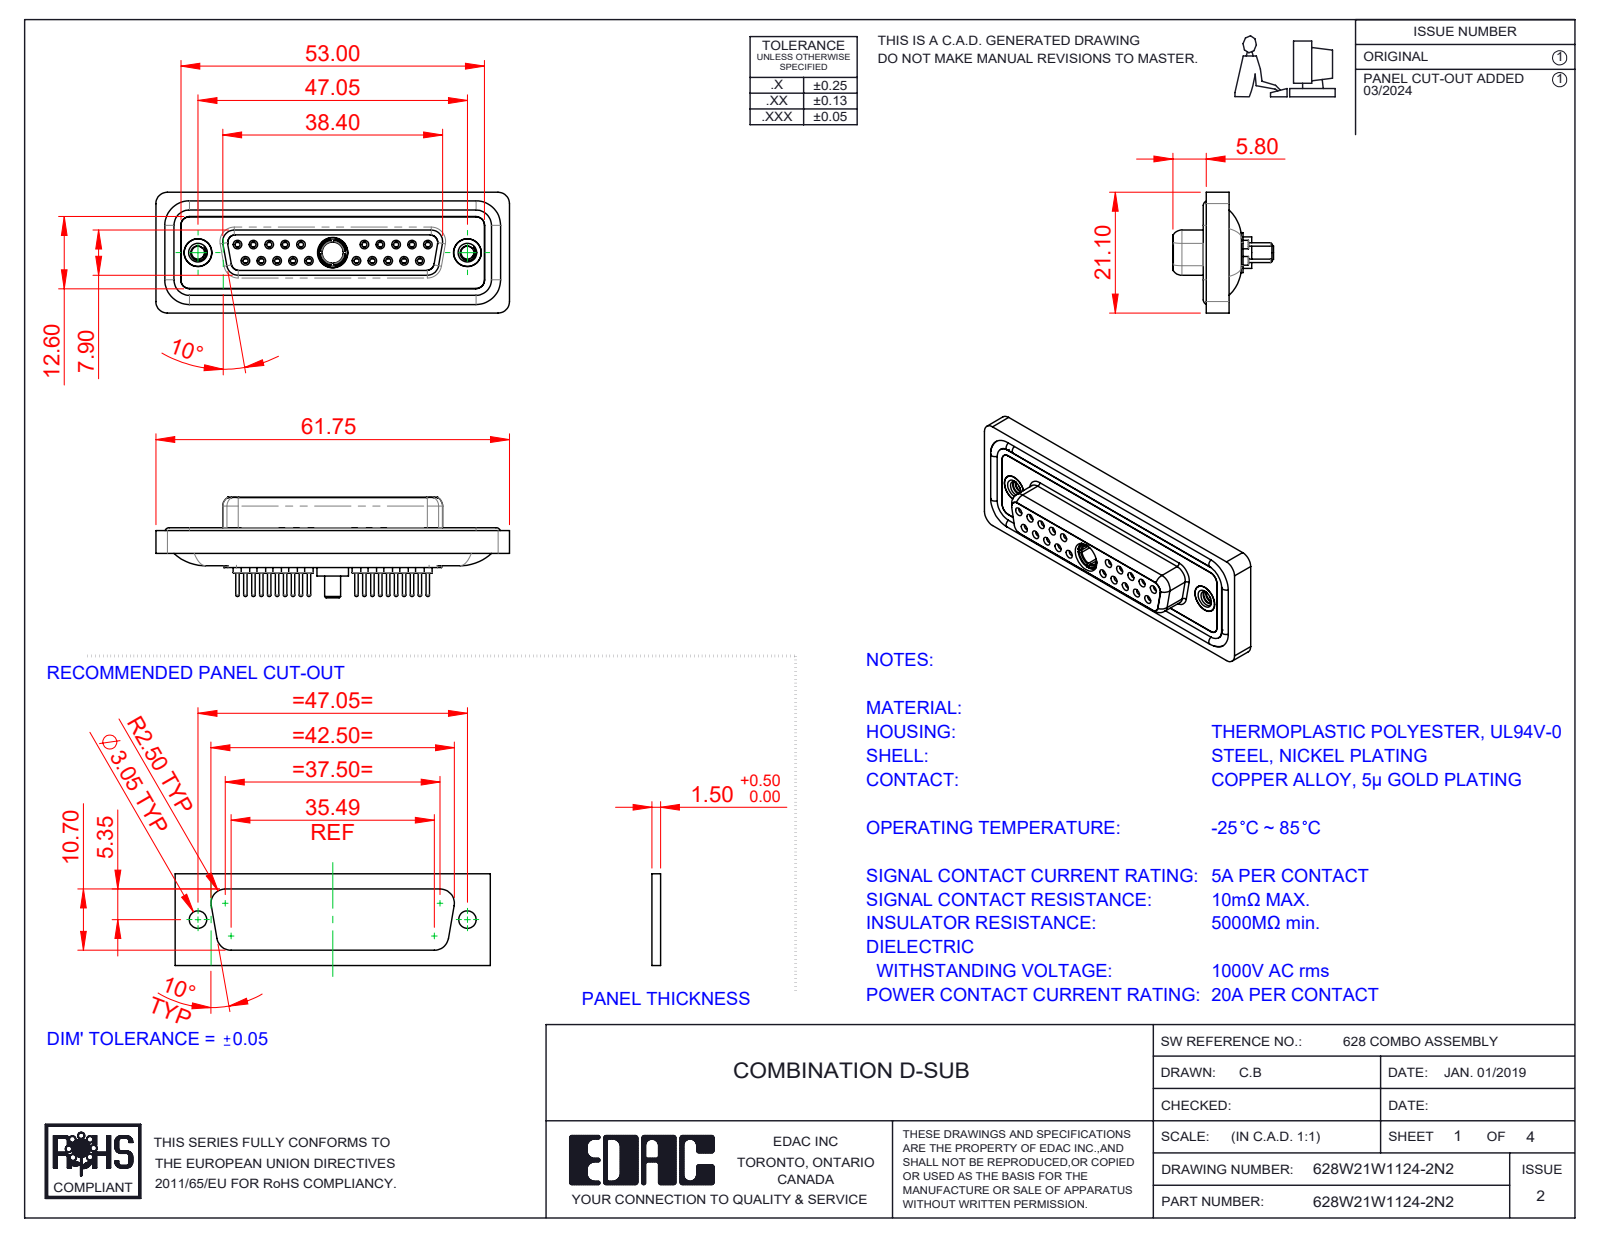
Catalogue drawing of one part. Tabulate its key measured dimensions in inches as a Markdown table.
| quantity | value |
| --- | --- |
| part name | 628Combo Contact Row 2_24; 628Combo Shell Front_25 Contacts; Power Socket_20A S; 628W21W1124-2N2 (+5 more) |
| STEP written by | SolidWorks 2023 (CONFIG_CONTROL_DESIGN) |
| units | inches |
| bodies | 29 solids, 1560 faces (434 planar, 591 cylindrical, 535 other) |
| overall size | 2.431 × 0.831 × 0.691 |
| volume | 0.511 in³ |
| surface area | 21.7 in² |
| round holes (diameter × count) | 0.035 × 20, 0.043 × 20, 0.059 × 20, 0.079 × 20, 0.063 × 10, 0.067 × 10, 0.191 × 3, 0.089 × 2, 0.157 × 2, 0.159 × 2, 0.197 × 2, 0.146 × 1 |
| round bosses / shafts (diameter × count) | 0.087 × 20, 0.024 × 20, 0.063 × 14, 0.195 × 2, 0.189 × 2, 0.217 × 1, 0.205 × 1, 0.195 × 1 |
| partial cylindrical surfaces (radius × count) | 0.059 × 22, 0.079 × 18, 0.053 × 8, 0.063 × 8, 0.01 × 4, 0.02 × 4, 0.024 × 4, 0.026 × 4 |
| main face-to-face distances | 0.016, 0.071, 0.293, 0.26, 0.222, 0.02, 0.063, 0.278, 0.114, 0.043 |
| hole center spacings | 0.124, 0.109, 0.218, 0.198, 0.327, 0.294, 0.654, 0.763 |
